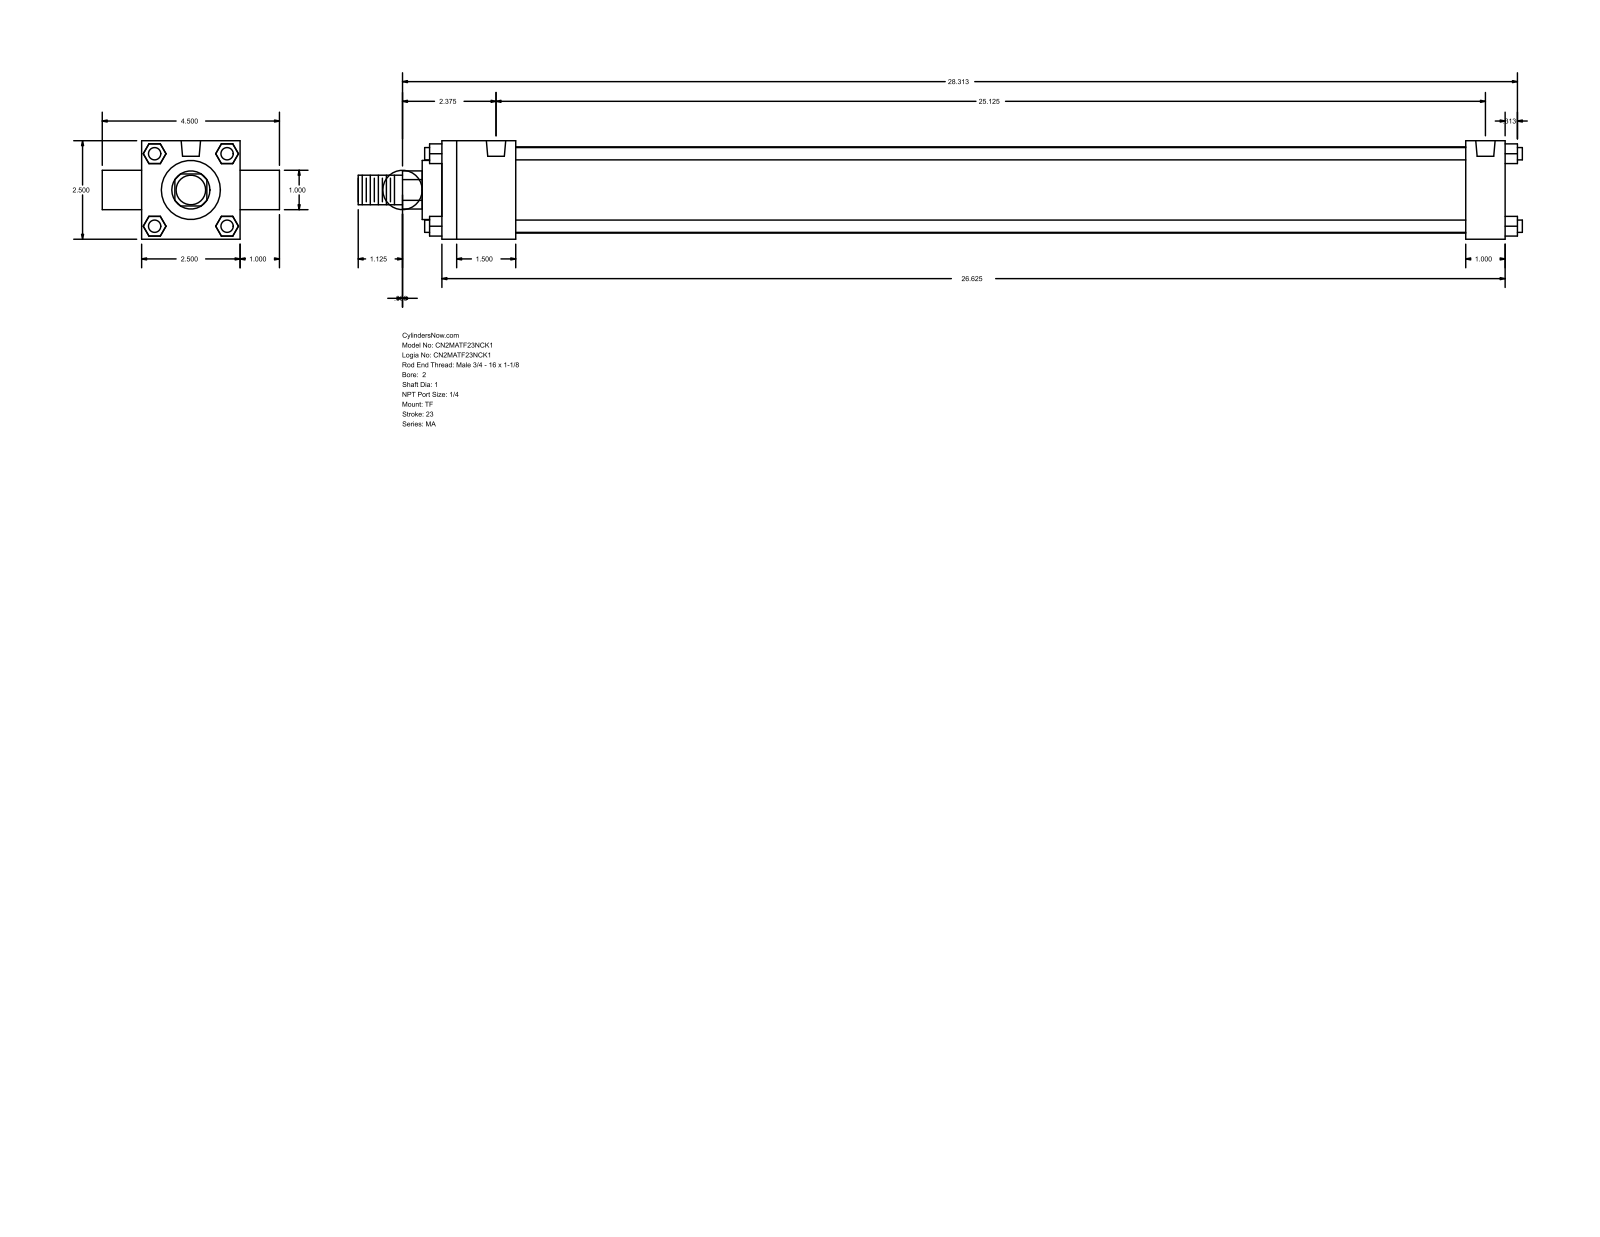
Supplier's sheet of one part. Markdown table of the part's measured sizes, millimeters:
| quantity | value |
| --- | --- |
| part name | MA_TF__0200_1 |
| STEP written by | GSSL Pune (CONFIG_CONTROL_DESIGN) |
| units | millimeters |
| bodies | 0 solids, 120 faces (92 planar, 28 cylindrical, 0 other) |
| overall size | 750.89 × 114.3 × 63.5 |
| round holes (diameter × count) | 7.94 × 3, 12.49 × 2 |
| round bosses / shafts (diameter × count) | 7.94 × 4, 25.4 × 2, 55.63 × 1, 38.1 × 1, 19.05 × 1 |
| partial cylindrical surfaces (radius × count) | 12.29 × 1 |
| main face-to-face distances | 63.5, 25.4, 685.8, 12.7, 47.63, 660.4, 612.77, 638.17, 88.9, 23.37 |
| hole center spacings | 638.17 |
